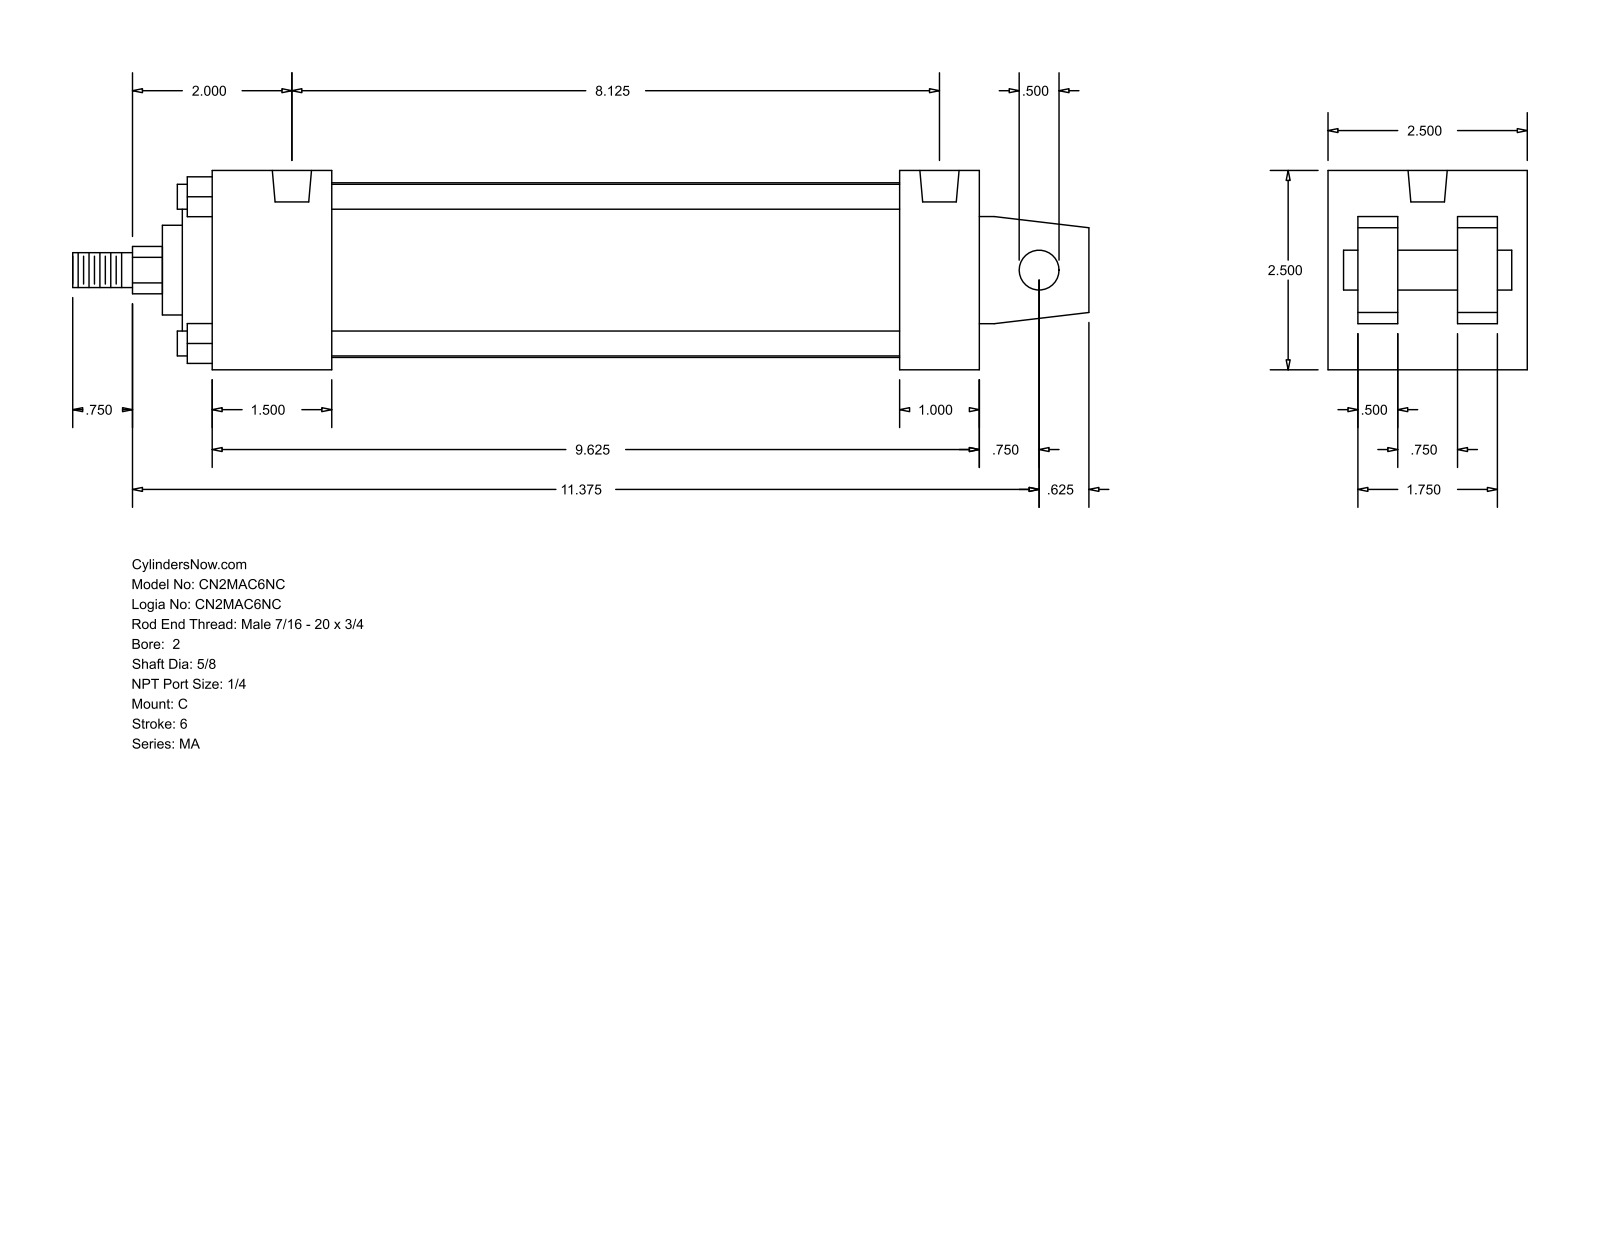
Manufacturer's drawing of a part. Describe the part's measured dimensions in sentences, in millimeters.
The part is named "MA_C__0200_0.625". Its 3-D file was written by "GSSL Pune (CONFIG_CONTROL_DESIGN)". It is 0 solids with 105 faces: 77 planar, 28 cylindrical and 0 other. Overall it measures 323.85 by 63.5 by 63.5 millimeters. Round holes: 4 of diameter 7.94, 2 of diameter 12.49. Round bosses or shafts: 4 of diameter 7.94, 1 of diameter 55.63, 1 of diameter 50.8, 1 of diameter 28.57, 1 of diameter 15.88, 1 of diameter 12.7, 1 of diameter 11.11. Partial cylindrical surfaces (rounded edges, fillets, slot ends): 1 of radius 7.54. The main face-to-face distances are 63.5, 9.52, 12.7, 22.22, 41.28, 53.98, 31.76, 38.1, 244.48, 206.38. The hole center spacings are 206.38.
